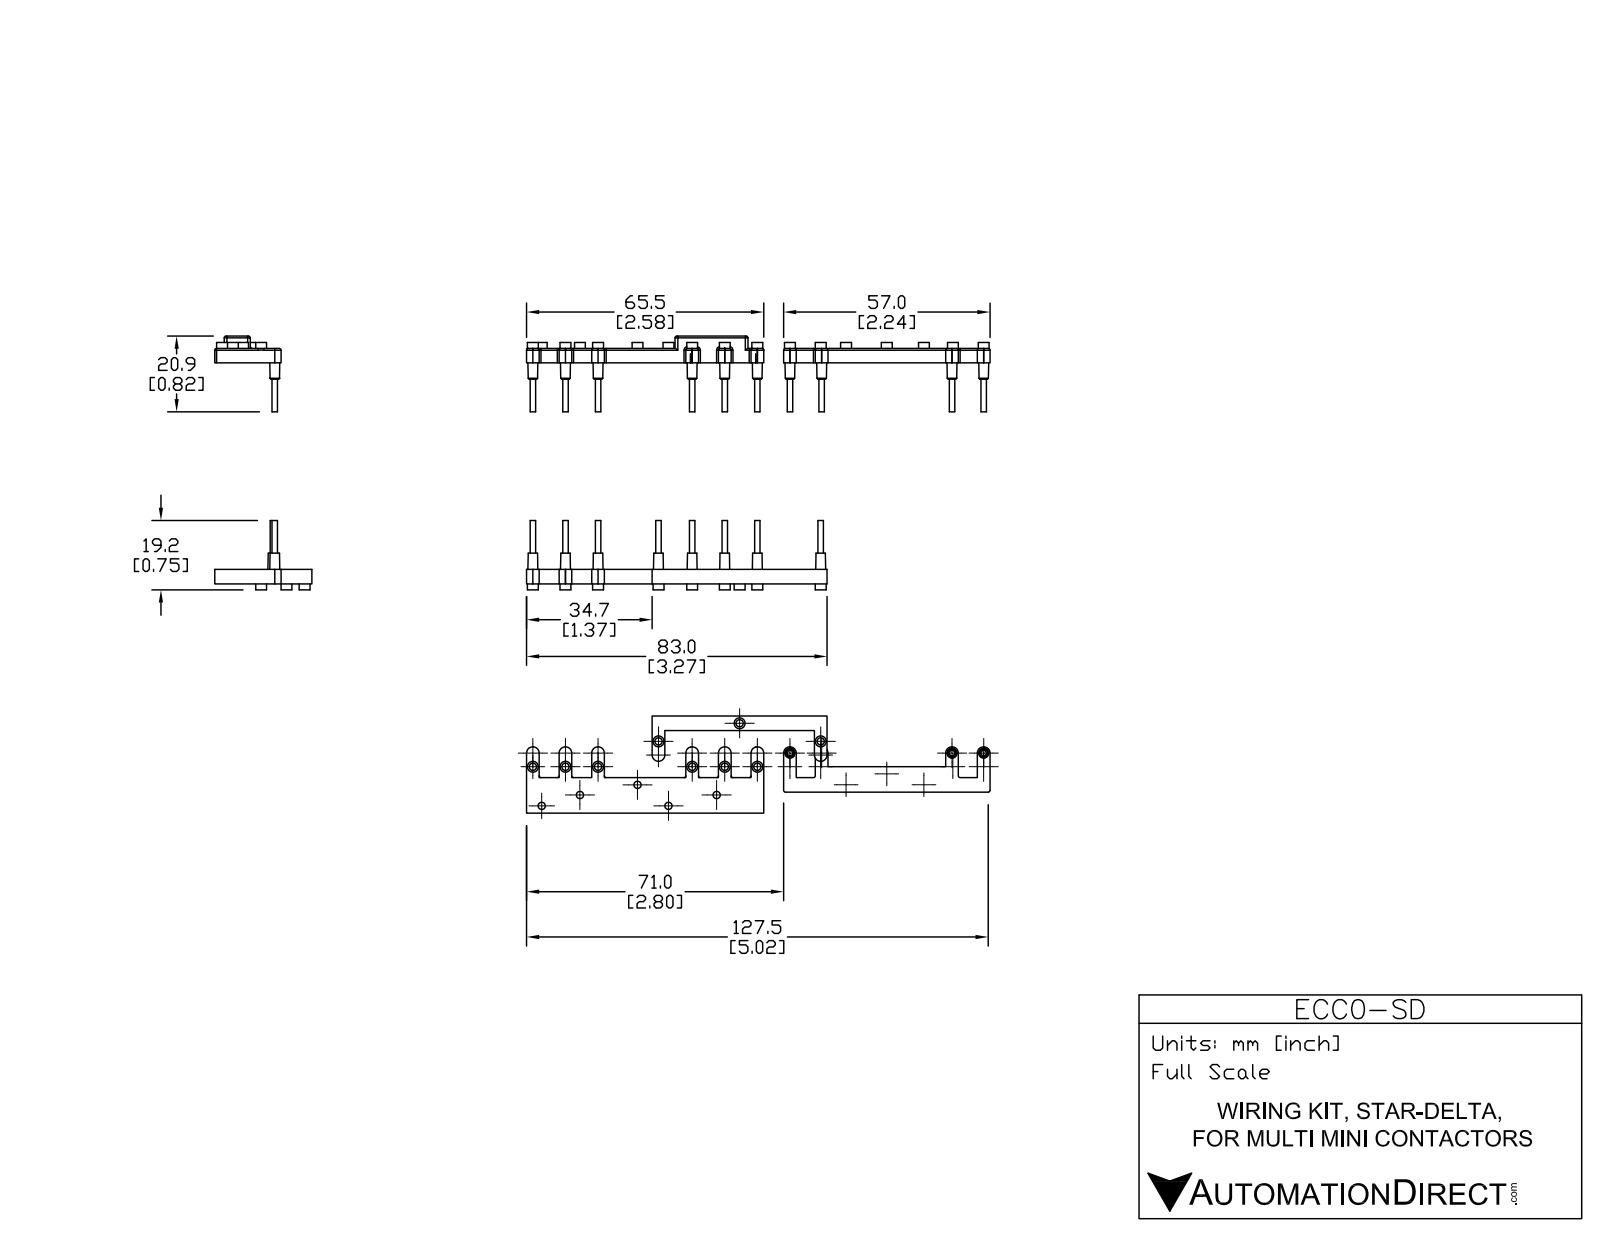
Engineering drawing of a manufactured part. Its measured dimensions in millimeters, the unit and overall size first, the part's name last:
Units: millimetres
Overall size (bounding box): 128 × 70.05 × 26.8
Round holes (diameter × count): ⌀2 ×21
Round bosses / shafts (diameter × count): ⌀3 ×20, ⌀1.5 ×12
Partial cylindrical surfaces — rounded edges, fillets, slot ends (radius × count): R0.5 ×47, R1.74 ×24, R0.75 ×6
Main face-to-face distances: 4, 61, 57, 65, 9, 9.8, 3.5, 17, 44, 18
Hole centre spacings: 9, 18, 18.36, 26.82, 35, 44, 53, 8.5
Volume: 10 453 mm³ · Surface area: 10 402 mm²
Bodies: 26 solids, 578 faces (201 planar, 268 cylindrical, 109 other)
Part name (STEP PRODUCT): ECC0-SD
STEP written by: SolidWorks 2013 (AUTOMOTIVE_DESIGN)
